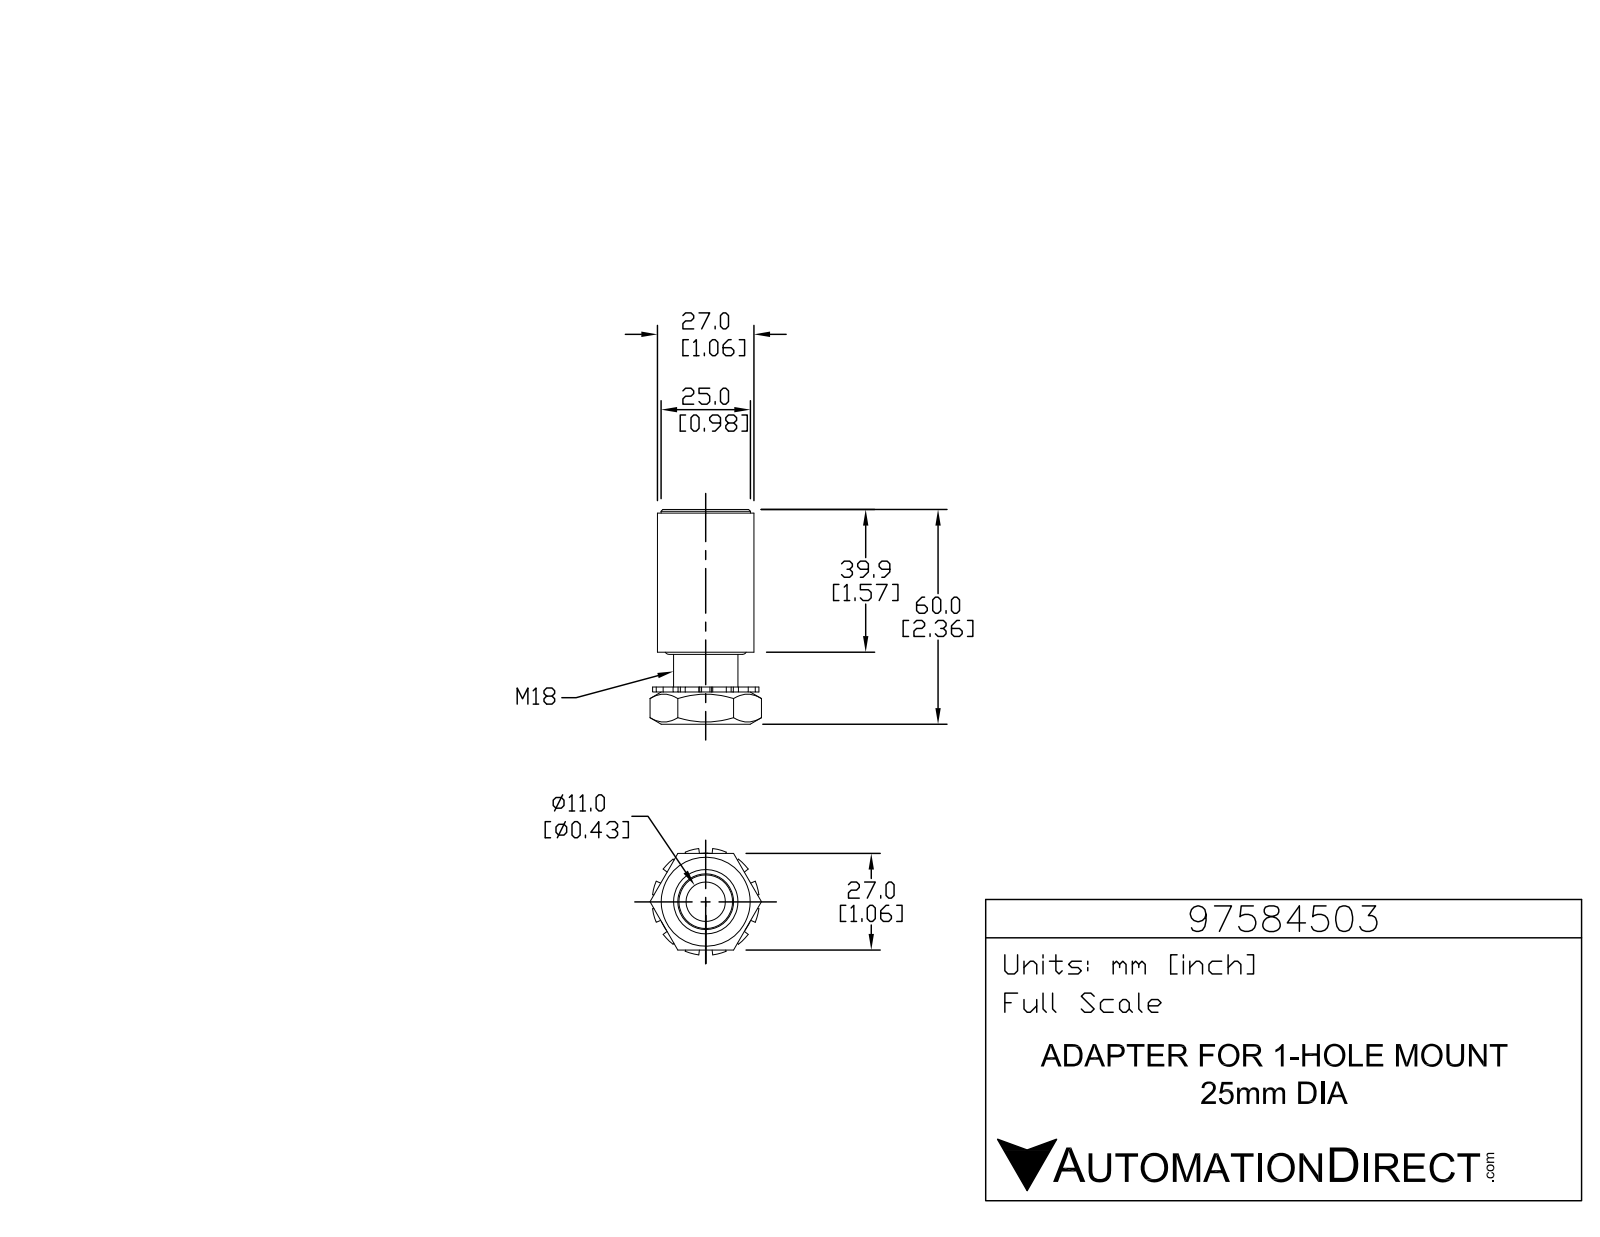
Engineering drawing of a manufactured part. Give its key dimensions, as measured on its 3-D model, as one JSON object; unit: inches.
{"part_name": "97584503", "step_written_by": "SolidWorks 2015 (AUTOMOTIVE_DESIGN)", "units": "inches", "bodies": {"solids": 4, "faces": 126, "planar": 42, "cylindrical": 60, "other": 24}, "overall_size": [2.362, 1.207, 1.167], "volume_in3": 0.906, "surface_area_in2": 18.23, "round_holes": [[0.435, 1], [0.754, 1], [0.863, 1], [0.943, 1]], "round_bosses_or_shafts": [[1.063, 1], [0.963, 1], [0.7, 1]], "partial_cylinders_radius": [[0.433, 1], [0.462, 1], [0.583, 1]], "face_to_face_distances": [1.045, 0.348, 0.436, 0.088, 0.381, 0.033, 0.055, 0.7, 0.352, 0.319]}
